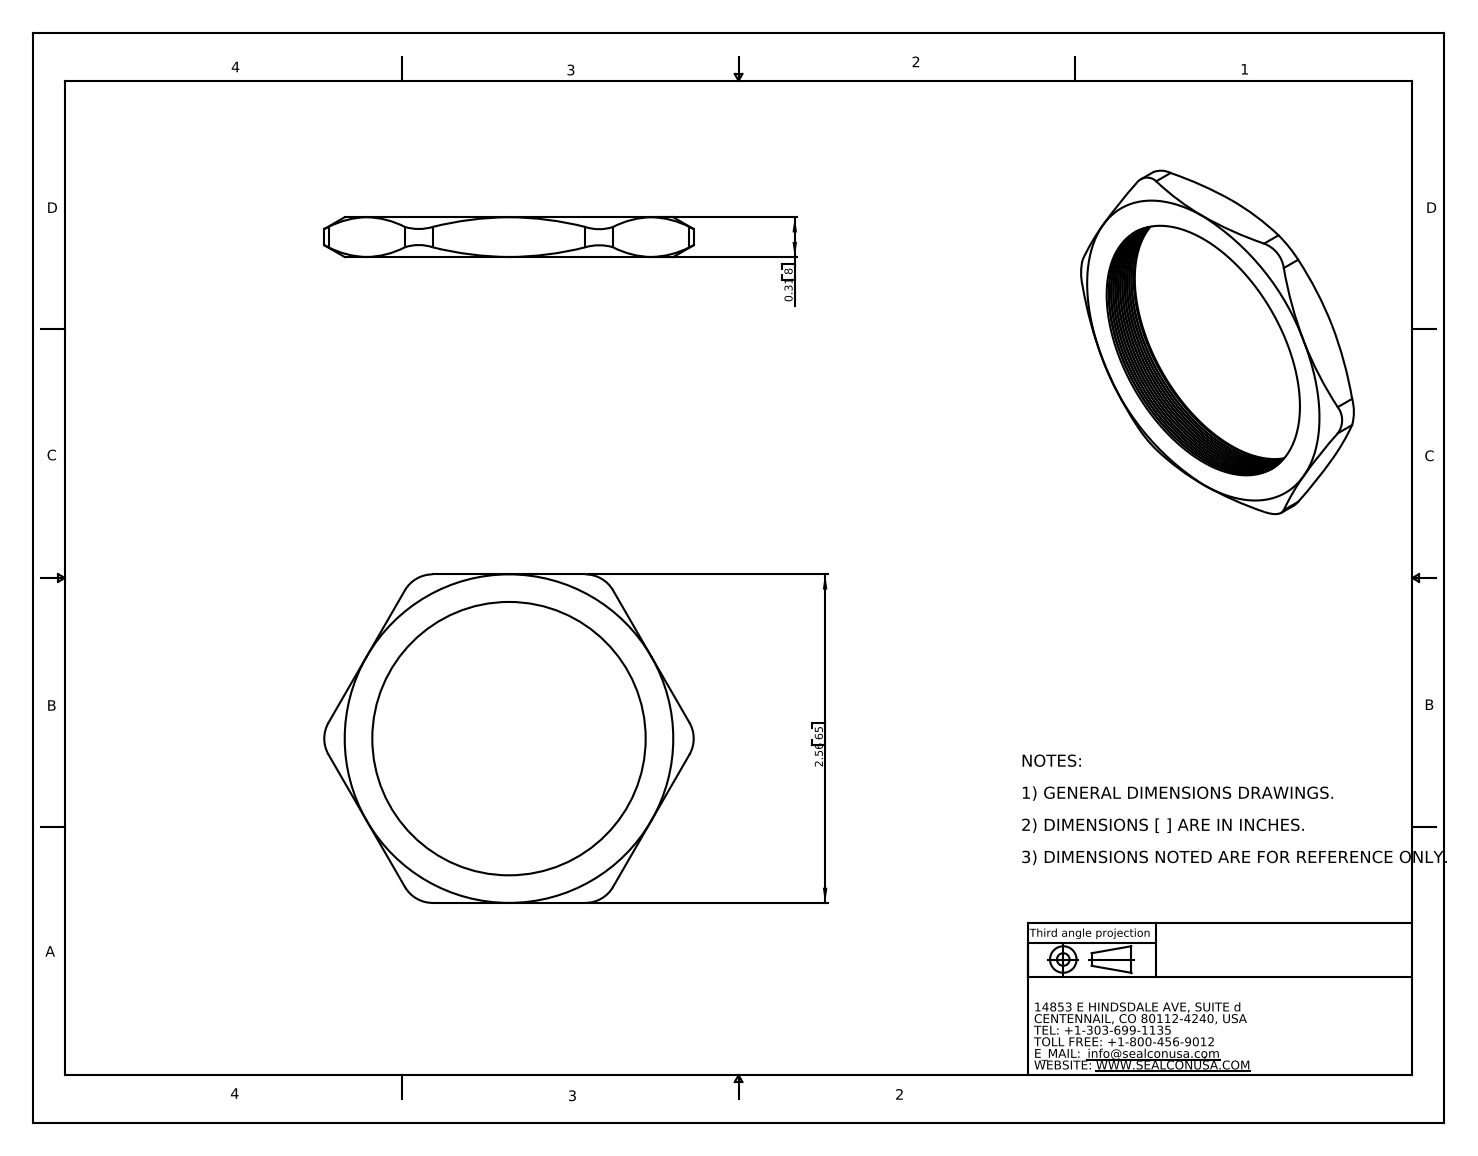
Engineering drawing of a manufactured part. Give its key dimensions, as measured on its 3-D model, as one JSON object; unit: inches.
{"part_name": "NP-42-GY", "step_written_by": "SolidWorks 2007 (CONFIG_CONTROL_DESIGN)", "units": "inches", "bodies": {"solids": 1, "faces": 101, "planar": 8, "cylindrical": 31, "other": 62}, "overall_size": [2.879, 2.56, 0.31], "volume_in3": 0.597, "surface_area_in2": 10.36, "round_holes": [[2.13, 1]], "partial_cylinders_radius": [[0.25, 6]], "face_to_face_distances": [0.31, 2.56]}
